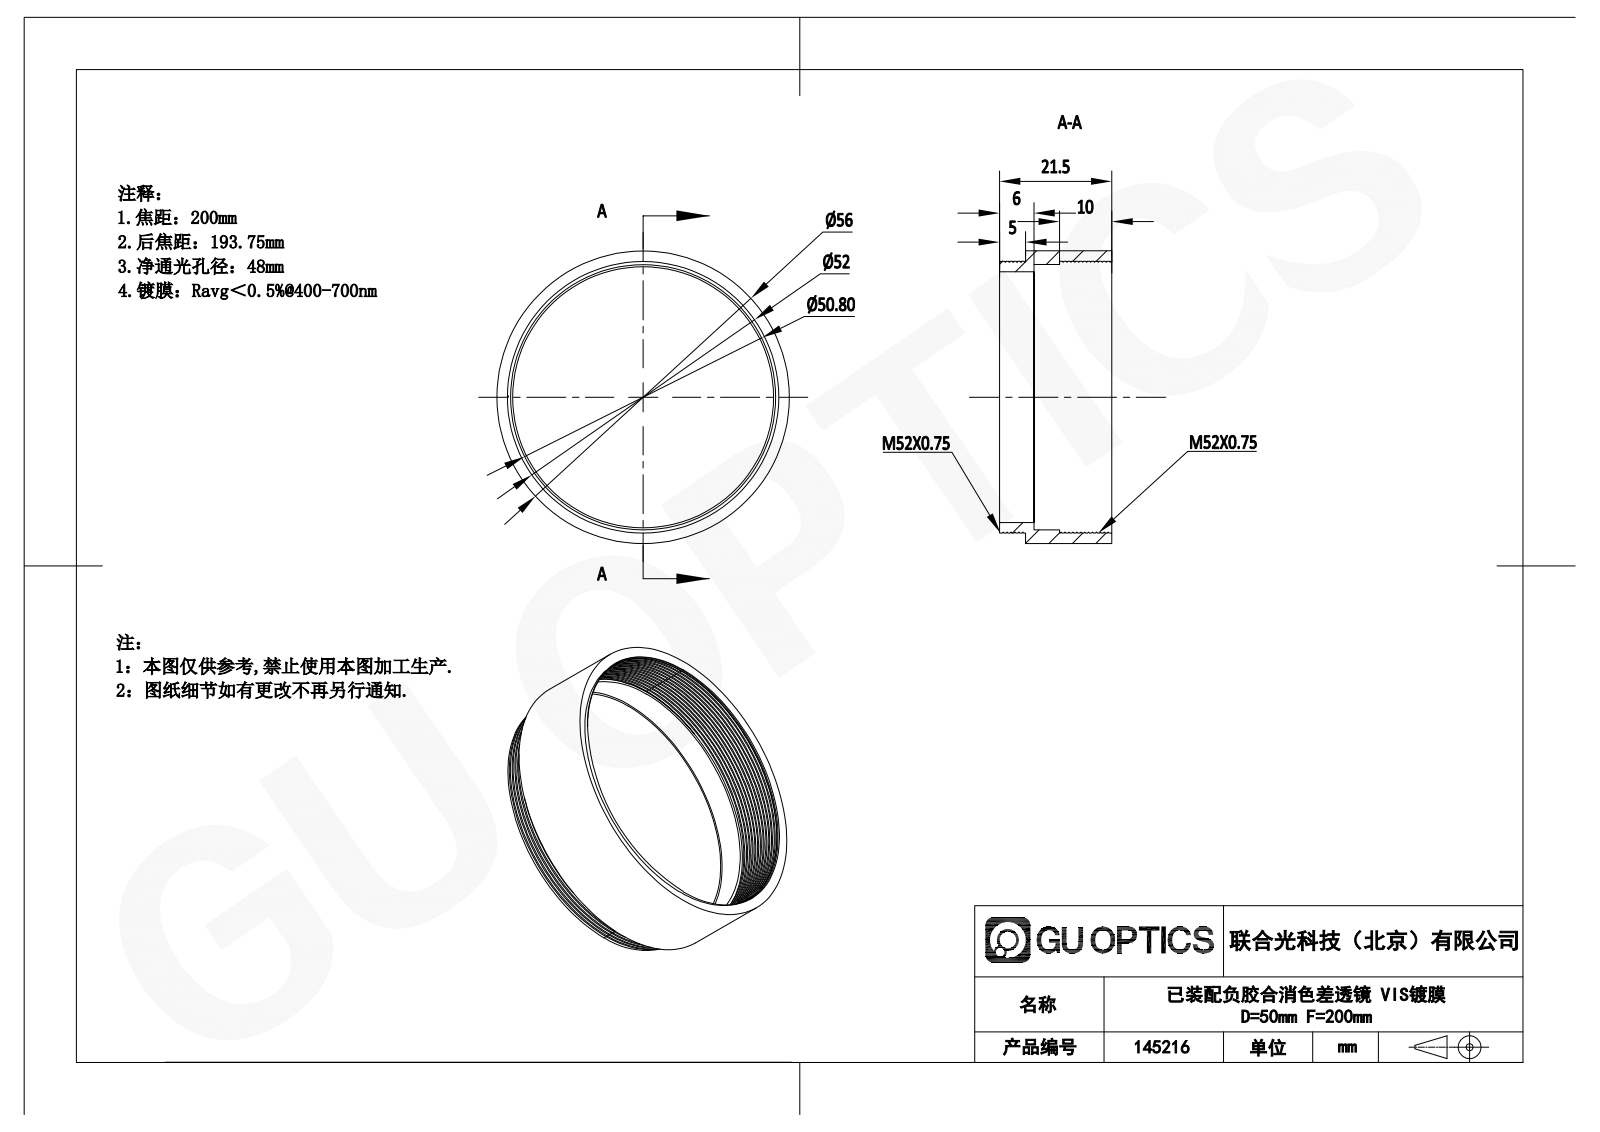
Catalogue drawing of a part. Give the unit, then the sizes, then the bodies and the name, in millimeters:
Units: millimetres
Overall size (bounding box): 56 × 56 × 21.5
Round holes (diameter × count): ⌀48 ×1, ⌀50.8 ×1, ⌀52 ×1
Round bosses / shafts (diameter × count): ⌀56 ×1, ⌀50 ×1
Main face-to-face distances: 1.58, 1.59, 16.5, 14.92, 14.91, 5, 6.58, 6.59, 21.5, 11.48
Volume: 8 187 mm³ · Surface area: 12 706 mm²
Bodies: 1 solid, 71 faces (11 planar, 53 cylindrical, 7 other)
Part name (STEP PRODUCT): APD-ML50-200-VIS
STEP written by: SolidWorks 2023 (CONFIG_CONTROL_DESIGN)
